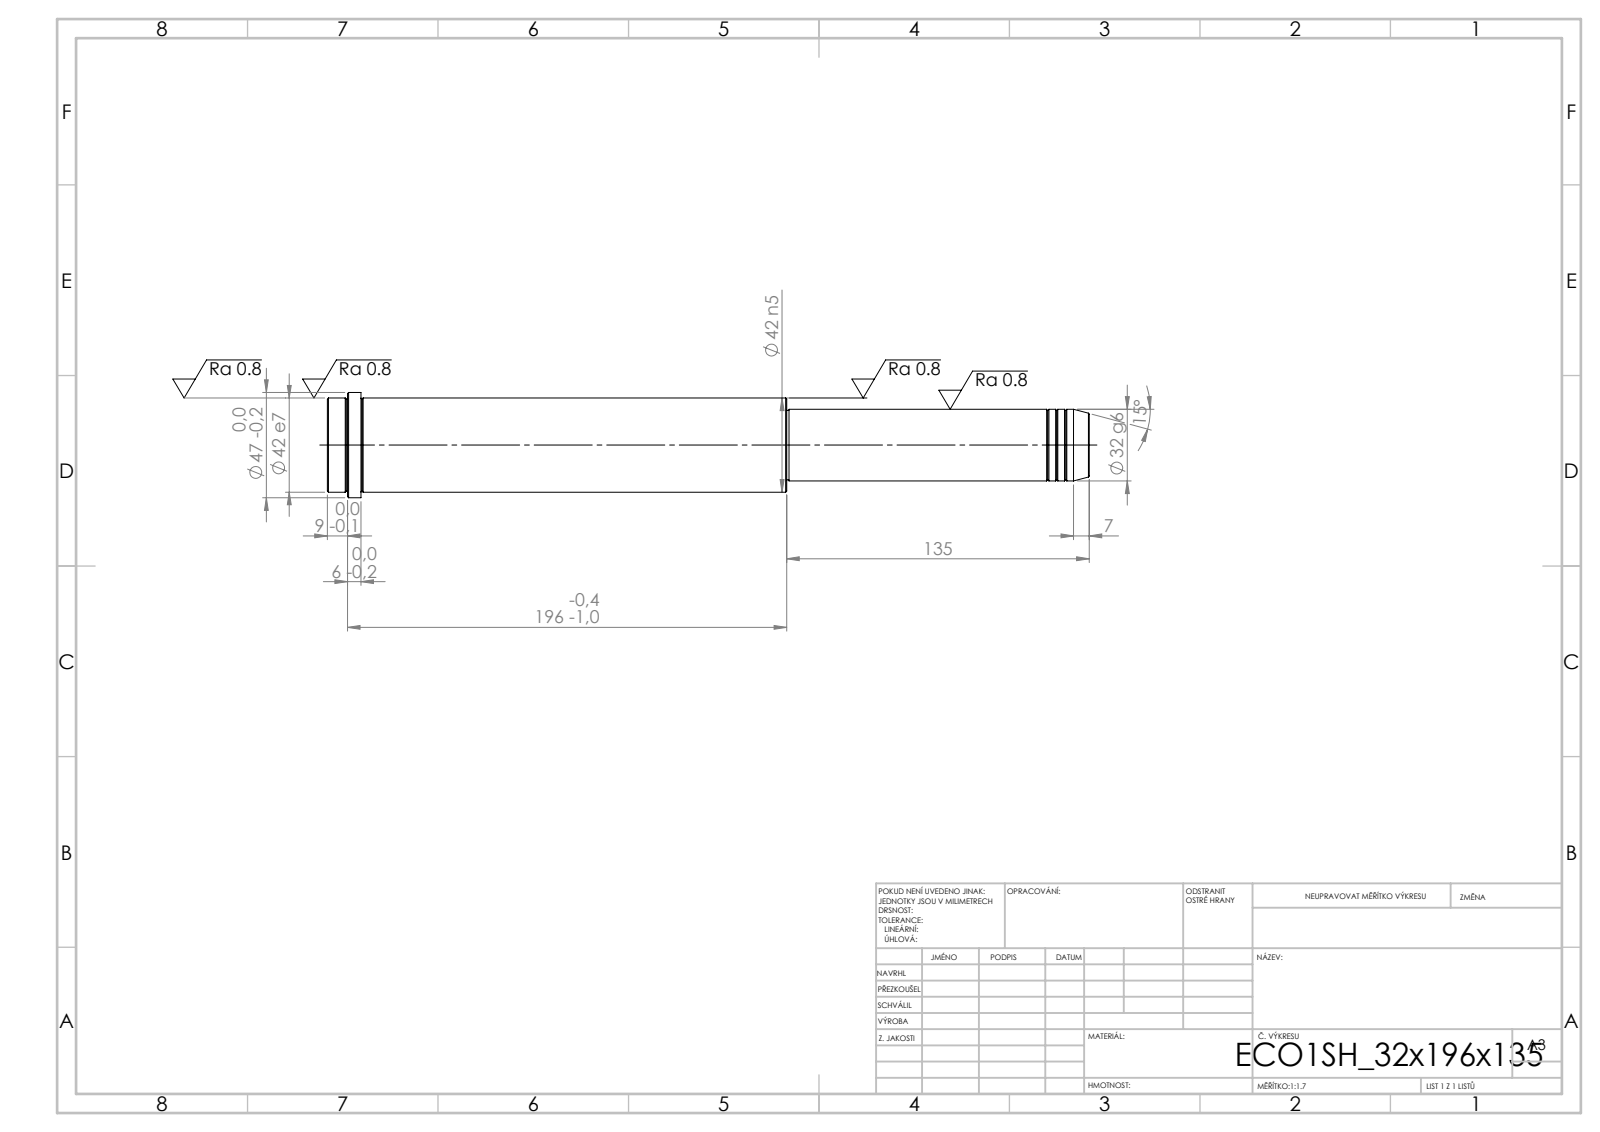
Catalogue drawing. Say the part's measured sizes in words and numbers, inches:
Its 3-D file was written by "SolidWorks 2019 (CONFIG_CONTROL_DESIGN)". It is 1 solid with 52 faces: 6 planar, 16 cylindrical and 30 other. Overall it measures 13.386 by 1.85 by 1.85 inches. Its volume is 24.03 cubic inches and its surface area 68.6 square inches. Round bosses or shafts: 1 of diameter 1.85, 1 of diameter 1.654, 1 of diameter 1.26, 1 of diameter 1.22. The main face-to-face distances are 13.386, 5.315, 8.071, 12.795, 7.48, 0.591, 13.031, 7.717, 0.236, 0.354.
